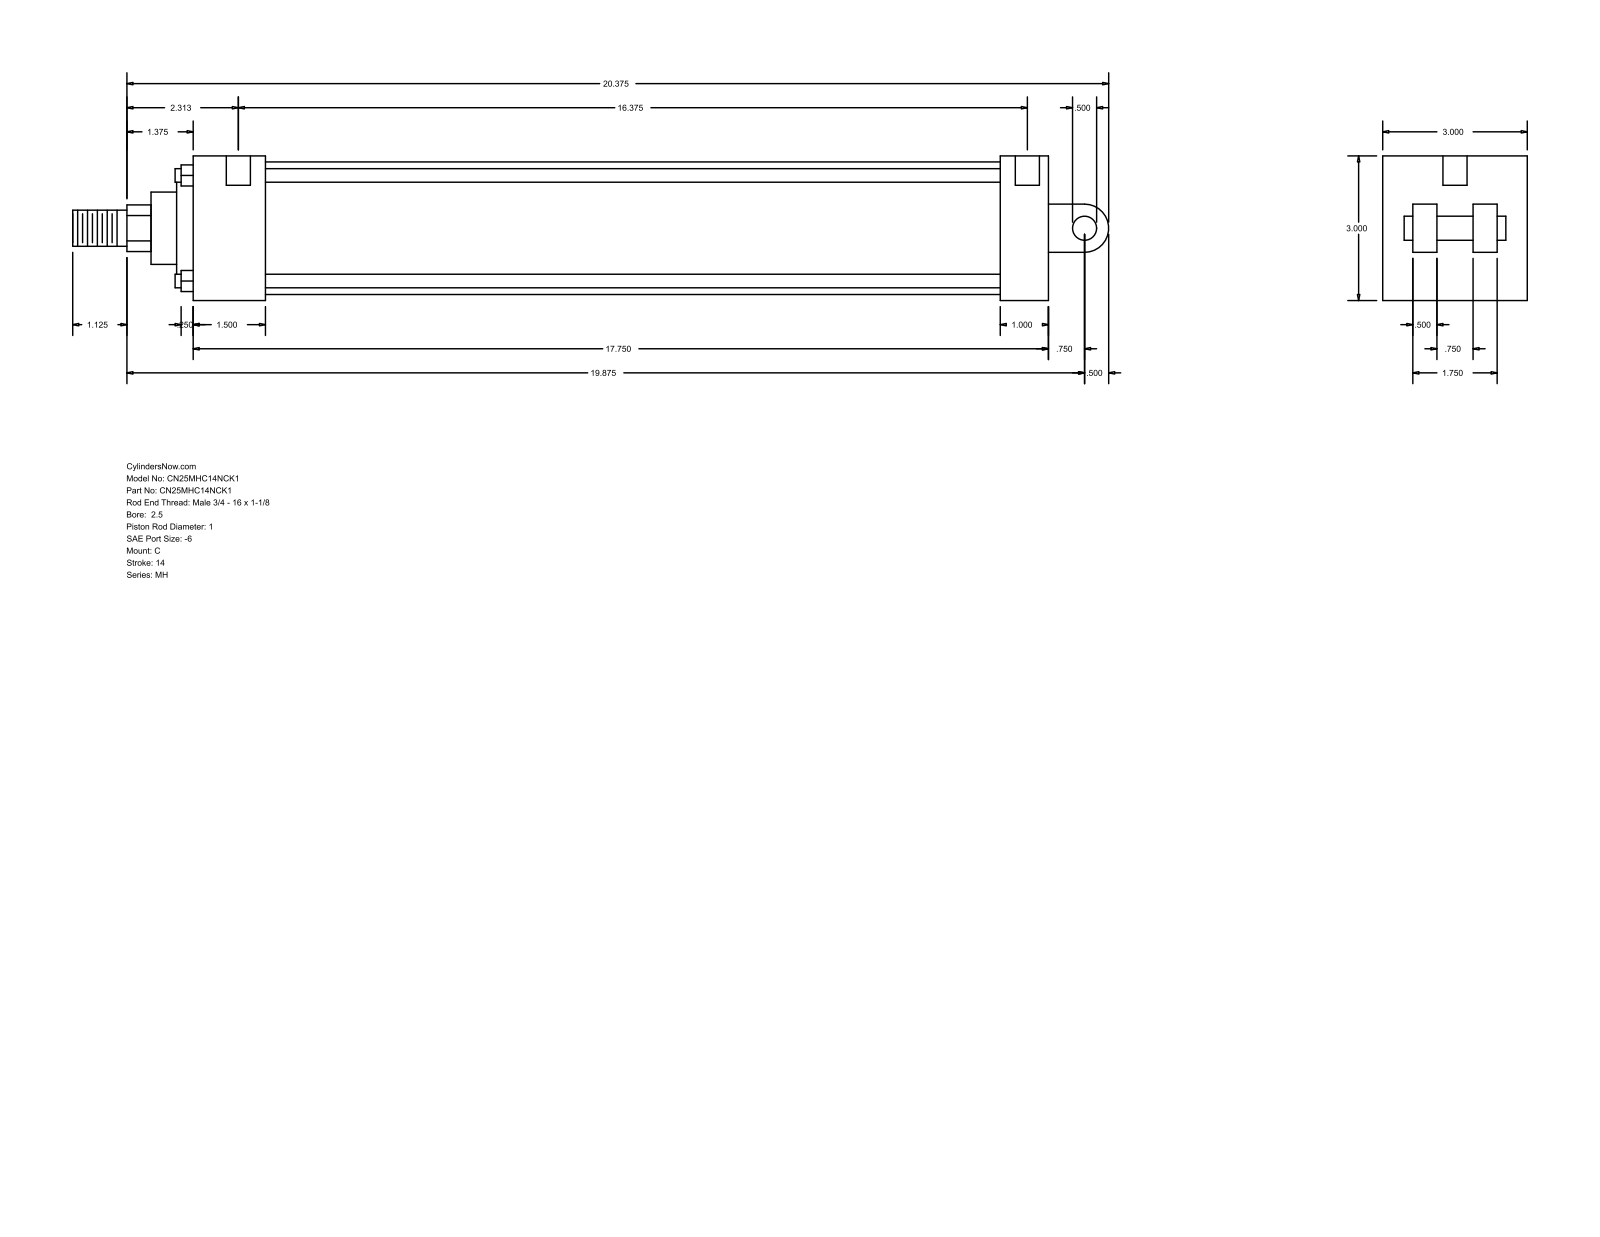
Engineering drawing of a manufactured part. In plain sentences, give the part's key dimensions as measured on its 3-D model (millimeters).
The part is named "MH_C__0250_1". Its 3-D file was written by "GSSL Pune (CONFIG_CONTROL_DESIGN)". It is 0 solids with 101 faces: 71 planar, 30 cylindrical and 0 other. Overall it measures 546.1 by 76.2 by 76.2 millimeters. Round holes: 4 of diameter 5.56, 2 of diameter 12.7. Round bosses or shafts: 4 of diameter 7.14, 1 of diameter 69.85, 1 of diameter 60.33, 1 of diameter 38.1, 1 of diameter 25.4, 1 of diameter 19.05, 1 of diameter 12.7. Partial cylindrical surfaces (rounded edges, fillets, slot ends): 1 of radius 12.29, 1 of radius 12.7. The main face-to-face distances are 76.2, 450.85, 25.39, 60.33, 15.87, 425.46, 38.11, 387.35, 412.74, 12.7. The hole center spacings are 423.86, 3.18, 4.76, 415.92, 419.1, 420.68.
